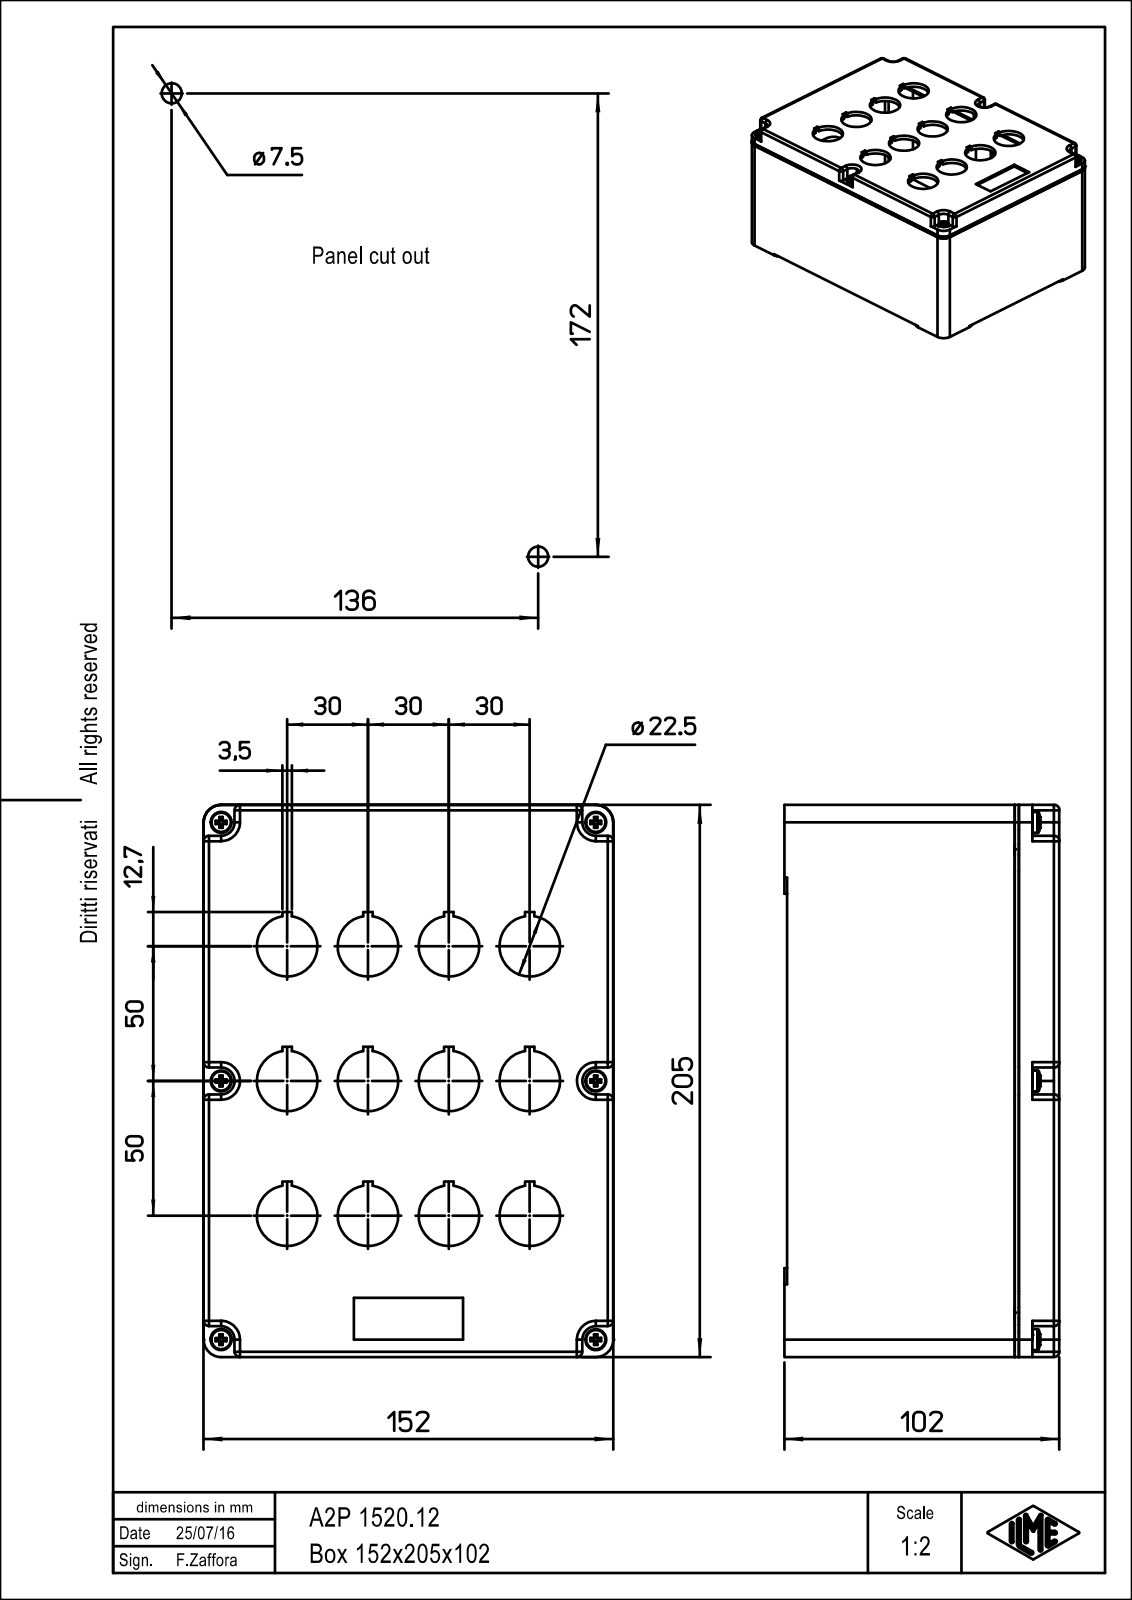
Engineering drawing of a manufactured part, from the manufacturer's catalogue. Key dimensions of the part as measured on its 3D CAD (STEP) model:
Part name (STEP PRODUCT): COVER; BOX; A2P_1520.12
STEP written by: PTC Creo Elements/Direct Modeling 19.0B 21-Mar-2015 (C) Parametric Technology GmbH (AUTOMOTIVE_DESIGN)
Units: millimetres
Bodies: 2 solids, 1179 faces (890 planar, 231 cylindrical, 58 other)
Overall size (bounding box): 205 × 152.02 × 102
Volume: 567 272 mm³ · Surface area: 284 037 mm²
Round holes (diameter × count): ⌀22.5 ×12, ⌀3.3 ×8, ⌀4.5 ×6, ⌀7.5 ×4, ⌀5.8 ×2, ⌀10.6 ×2, ⌀10.61 ×2
Round bosses / shafts (diameter × count): ⌀7.8 ×6, ⌀4 ×6, ⌀6.2 ×2, ⌀6 ×2, ⌀7 ×1
Partial cylindrical surfaces — rounded edges, fillets, slot ends (radius × count): R2 ×23, R0.33 ×22, R6 ×12, R6.5 ×12, R8 ×10, R5 ×6, R0.27 ×4, R0.27 ×4
Main face-to-face distances: 3, 98, 101, 95, 4.38, 4.37, 152, 205, 13.5, 147.63
Hole centre spacings: 58.31, 139, 30, 168.93, 50, 78.1, 137.86, 60
